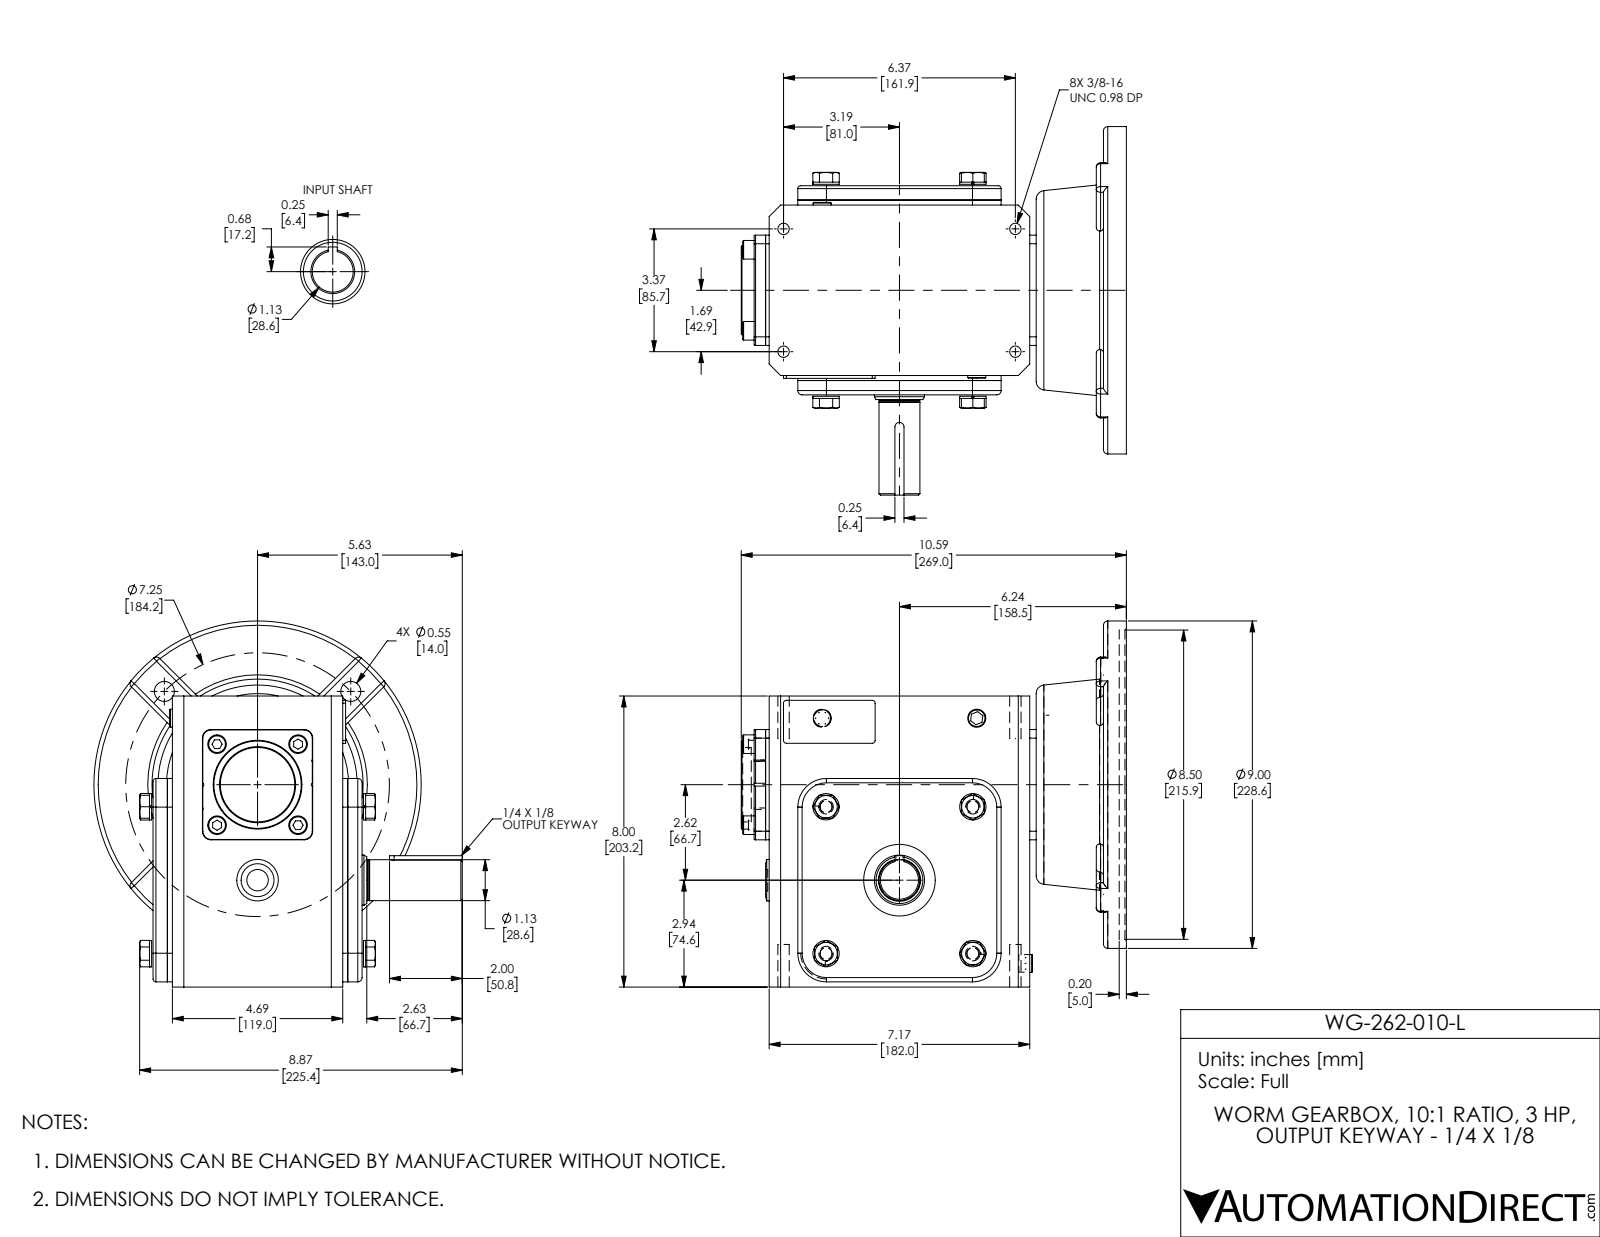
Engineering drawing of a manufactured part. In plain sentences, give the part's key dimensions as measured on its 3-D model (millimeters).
The part is named "WG-262-010-L". Its 3-D file was written by "SolidWorks 2017 (AUTOMOTIVE_DESIGN)". It is 31 solids with 552 faces: 299 planar, 136 cylindrical and 117 other. Overall it measures 269 by 257.3 by 255.6 millimeters. Its volume is 5 398 000 cubic millimeters and its surface area 484 500 square millimeters. Round holes: 4 of diameter 8, 4 of diameter 14, 1 of diameter 15, 1 of diameter 28.6, 1 of diameter 35, 1 of diameter 50, 1 of diameter 52, 1 of diameter 97, 1 of diameter 215.9. Round bosses or shafts: 4 of diameter 18.4, 4 of diameter 13, 1 of diameter 228.6, 1 of diameter 62, 1 of diameter 45, 1 of diameter 29, 1 of diameter 28.6, 1 of diameter 28.3. Partial cylindrical surfaces (rounded edges, fillets, slot ends): 15 of radius 3, 11 of radius 2, 4 of radius 6, 4 of radius 20, 2 of radius 0.5, 2 of radius 1, 1 of radius 3.2. The main face-to-face distances are 126, 10, 136, 13.5, 132.5, 3.5, 122.5, 203.2, 11, 146. The hole center spacings are 92.1, 130.2, 65.1, 85.7, 147, 161.9, 183.2, 184.2.
